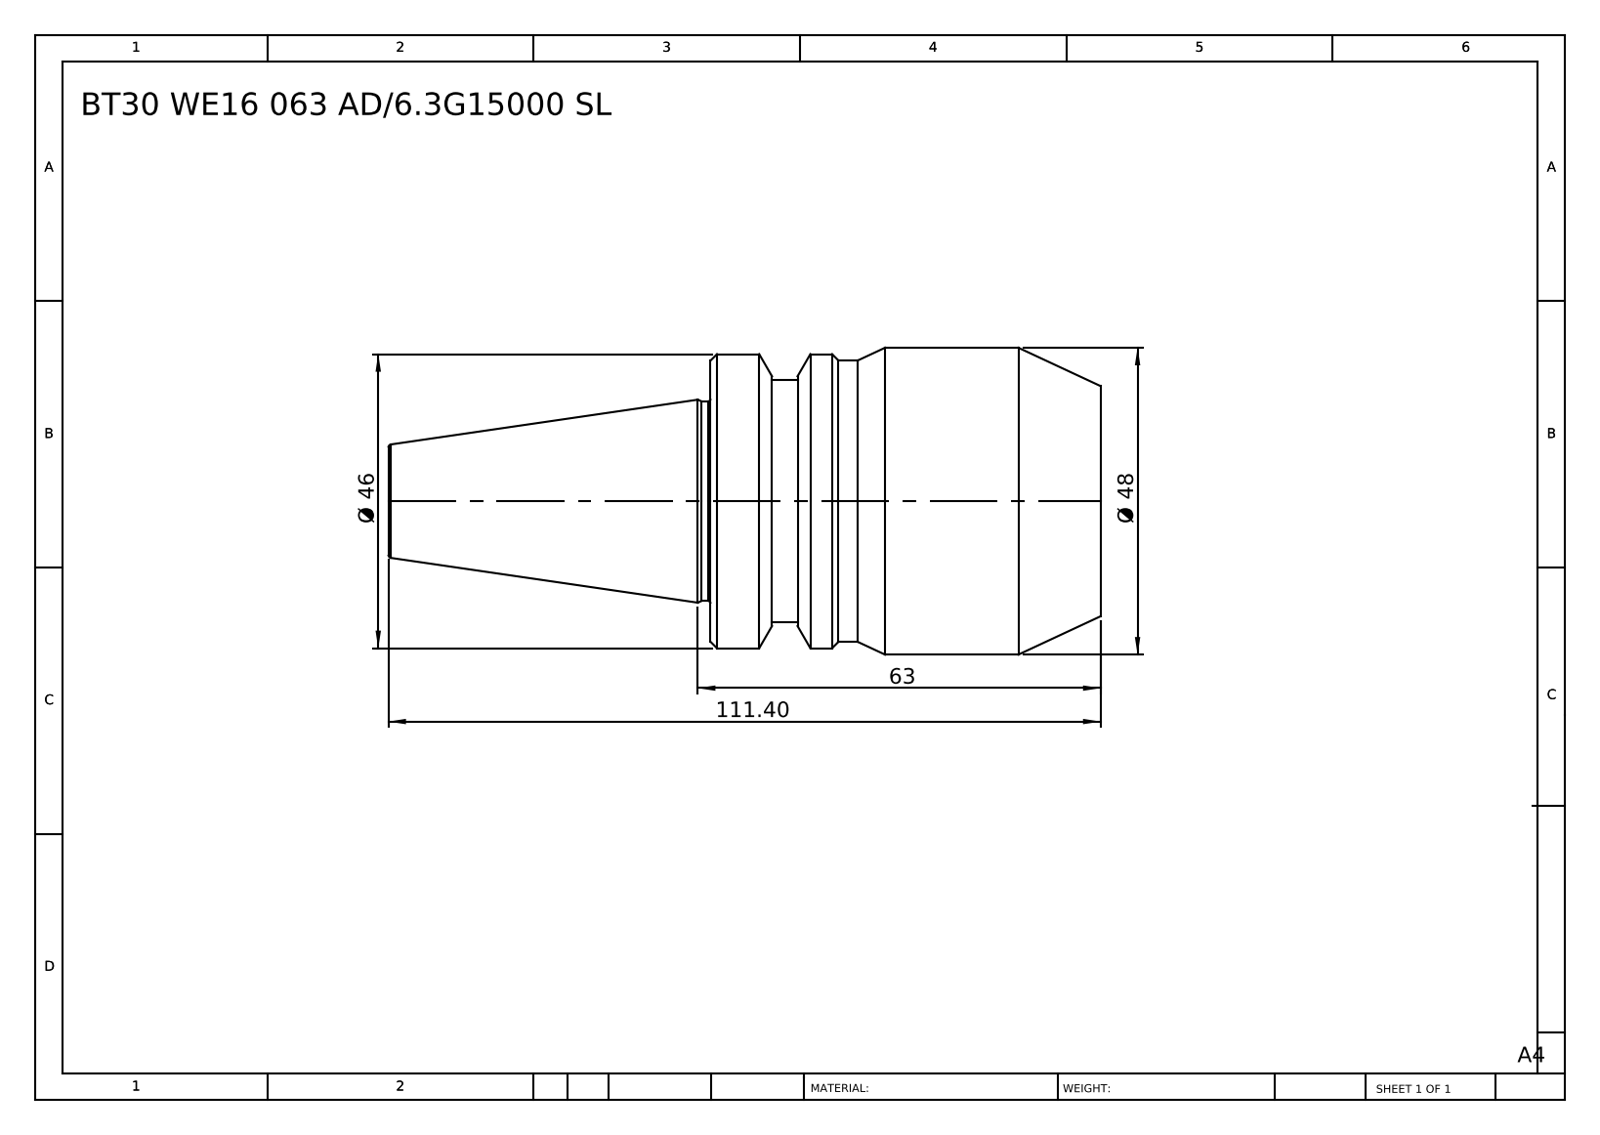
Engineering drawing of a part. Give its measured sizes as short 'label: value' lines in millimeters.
name: BT30 WE16 063 AD-6.3G15000 SL
written by: SolidWorks 2014 (CONFIG_CONTROL_DESIGN)
unit: mm
bodies: 1 solid, 37 faces (5 planar, 12 cylindrical, 20 other)
size: 111.4 × 48 × 48
volume: 122 739 mm³; area: 15 626 mm²
bosses: 1× ⌀48, 1× ⌀46, 1× ⌀44, 1× ⌀38, 1× ⌀31.2
face distances: 61, 111.4, 50.4, 51.4, 9.6, 60, 47.4, 4, 13.6, 64
